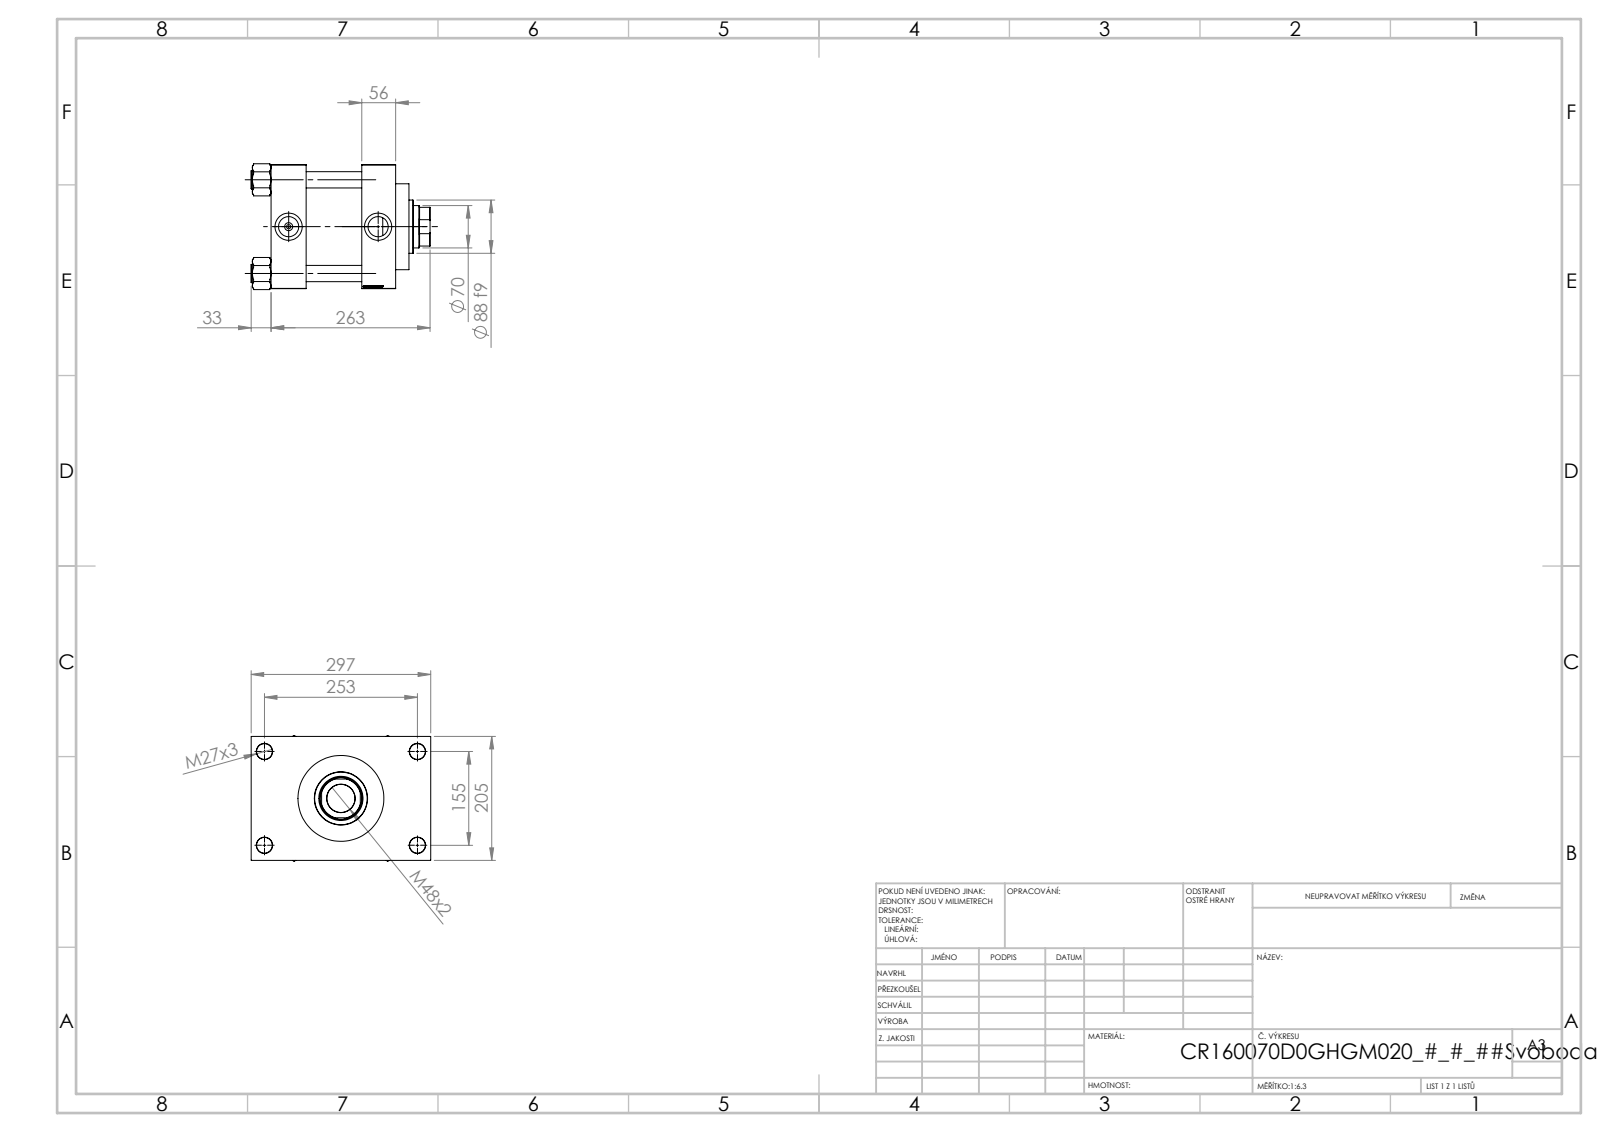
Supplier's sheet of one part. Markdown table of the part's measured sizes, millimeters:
| quantity | value |
| --- | --- |
| part name | V215CR_D_TYCINKA; V215CR_VCP_D; V215CR_D_Body; V215_VC_A (+1 more) |
| STEP written by | SolidWorks 2019 (CONFIG_CONTROL_DESIGN) |
| units | millimeters |
| bodies | 11 solids, 1148 faces (544 planar, 86 cylindrical, 518 other) |
| overall size | 297 × 296 × 208.14 |
| volume | 7 856 000 mm³ |
| surface area | 729 764 mm² |
| round holes (diameter × count) | 26 × 4, 27 × 4, 7 × 2, 33.24 × 2, 45 × 2, 46.5 × 1, 70 × 1, 73 × 1, 120 × 1, 142 × 1, 160 × 1 |
| round bosses / shafts (diameter × count) | 30 × 4, 166 × 1, 88 × 1 |
| partial cylindrical surfaces (radius × count) | 34 × 1 |
| main face-to-face distances | 58, 150, 92, 206, 148, 56, 205, 46, 251, 72 |
| hole center spacings | 49.05, 109.53, 148.35, 154.9, 162.53, 203.95, 256.13, 155 |
